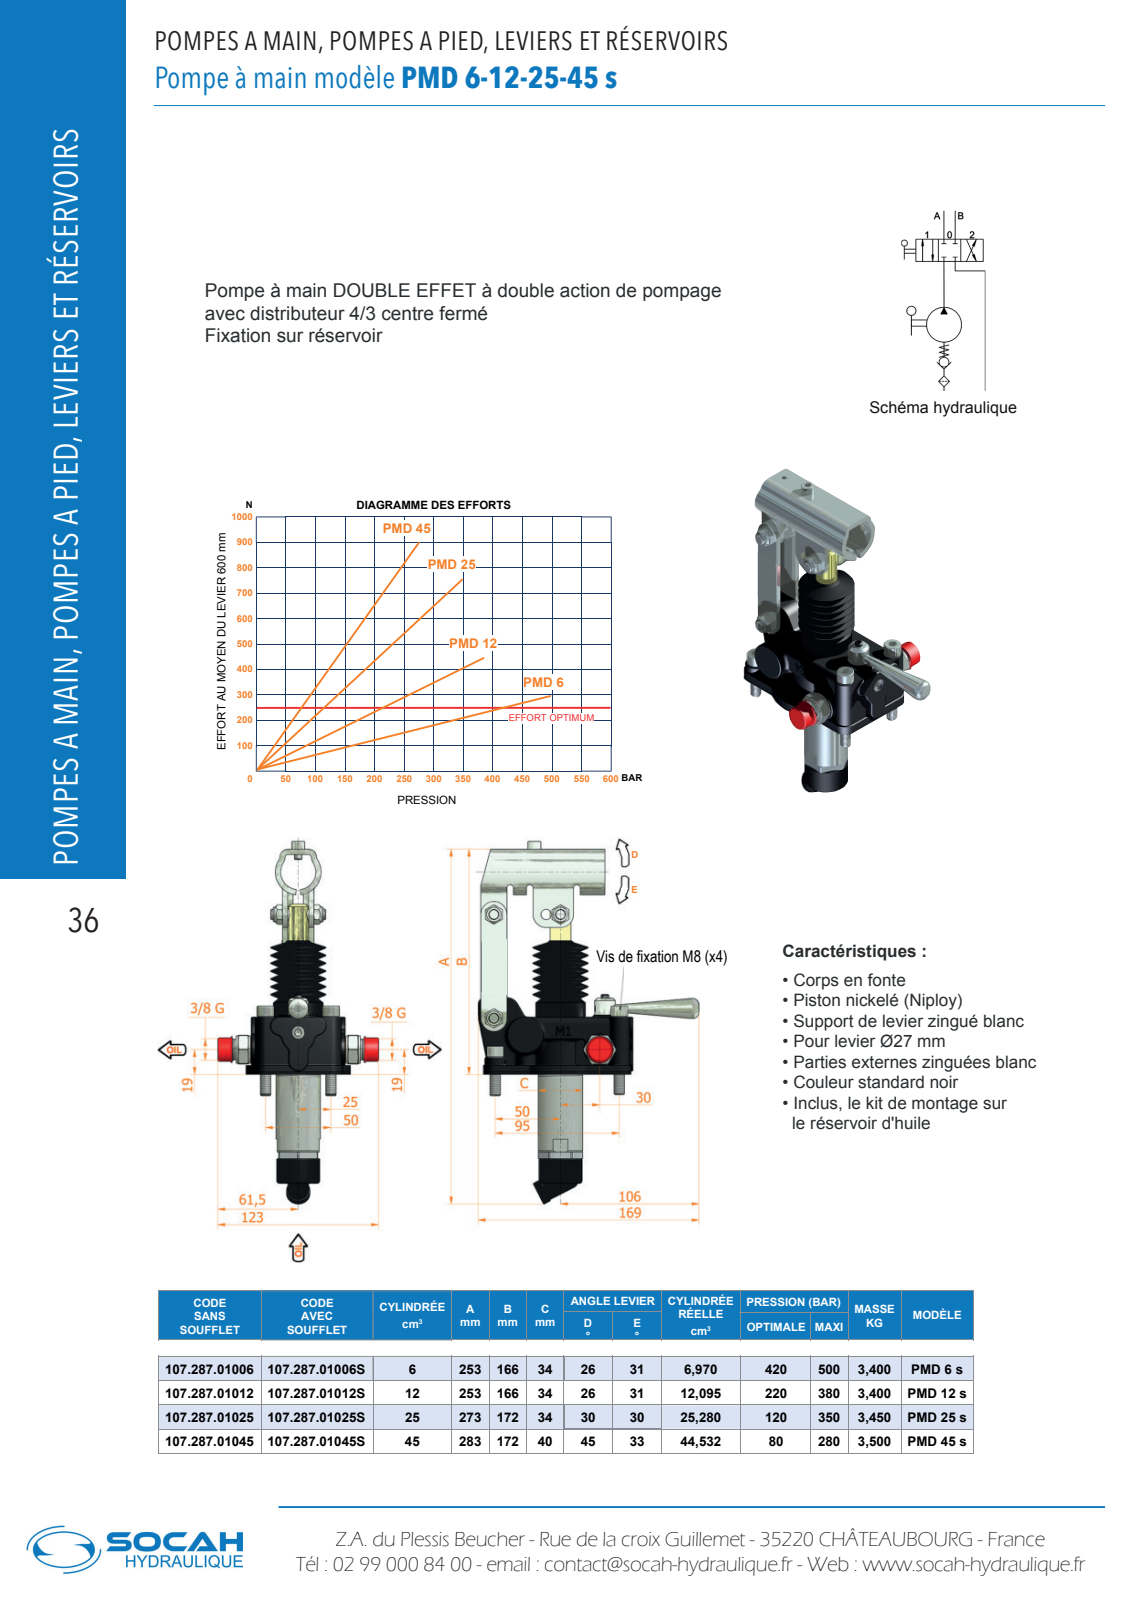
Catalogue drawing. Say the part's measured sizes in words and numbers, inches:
The part is named "6056.0045.10.50 Derivazione 2". Its 3-D file was written by "Autodesk Inventor 2013 (AUTOMOTIVE_DESIGN)". It is 14 solids with 1506 faces: 696 planar, 339 cylindrical and 471 other. Overall it measures 10.939 by 6.654 by 4.843 inches. Its volume is 0.603 cubic inches and its surface area 225.3 square inches. Round holes: 6 of diameter 0.315, 4 of diameter 0.551, 2 of diameter 0.194, 2 of diameter 0.197, 1 of diameter 0.157, 1 of diameter 0.354, 1 of diameter 0.394, 1 of diameter 0.531, 1 of diameter 0.63, 1 of diameter 0.787, 1 of diameter 0.984, 1 of diameter 1.181. Round bosses or shafts: 4 of diameter 0.512, 4 of diameter 0.472, 4 of diameter 0.335, 3 of diameter 0.709, 3 of diameter 0.435, 3 of diameter 0.315, 3 of diameter 0.236, 2 of diameter 0.787. Partial cylindrical surfaces (rounded edges, fillets, slot ends): 30 of radius 0.039, 24 of radius 0.008, 16 of radius 0.004, 16 of radius 0.197, 14 of radius 0.079, 9 of radius 0.118, 9 of radius 0.315, 6 of radius 0.014. The main face-to-face distances are 0.157, 0.787, 0.079, 0.197, 1.457, 0.63, 1.732, 0.945, 0.276, 1.654. The hole center spacings are 1.004, 1.075, 1.969, 2.027, 2.201, 3.45, 3.678, 3.74.
